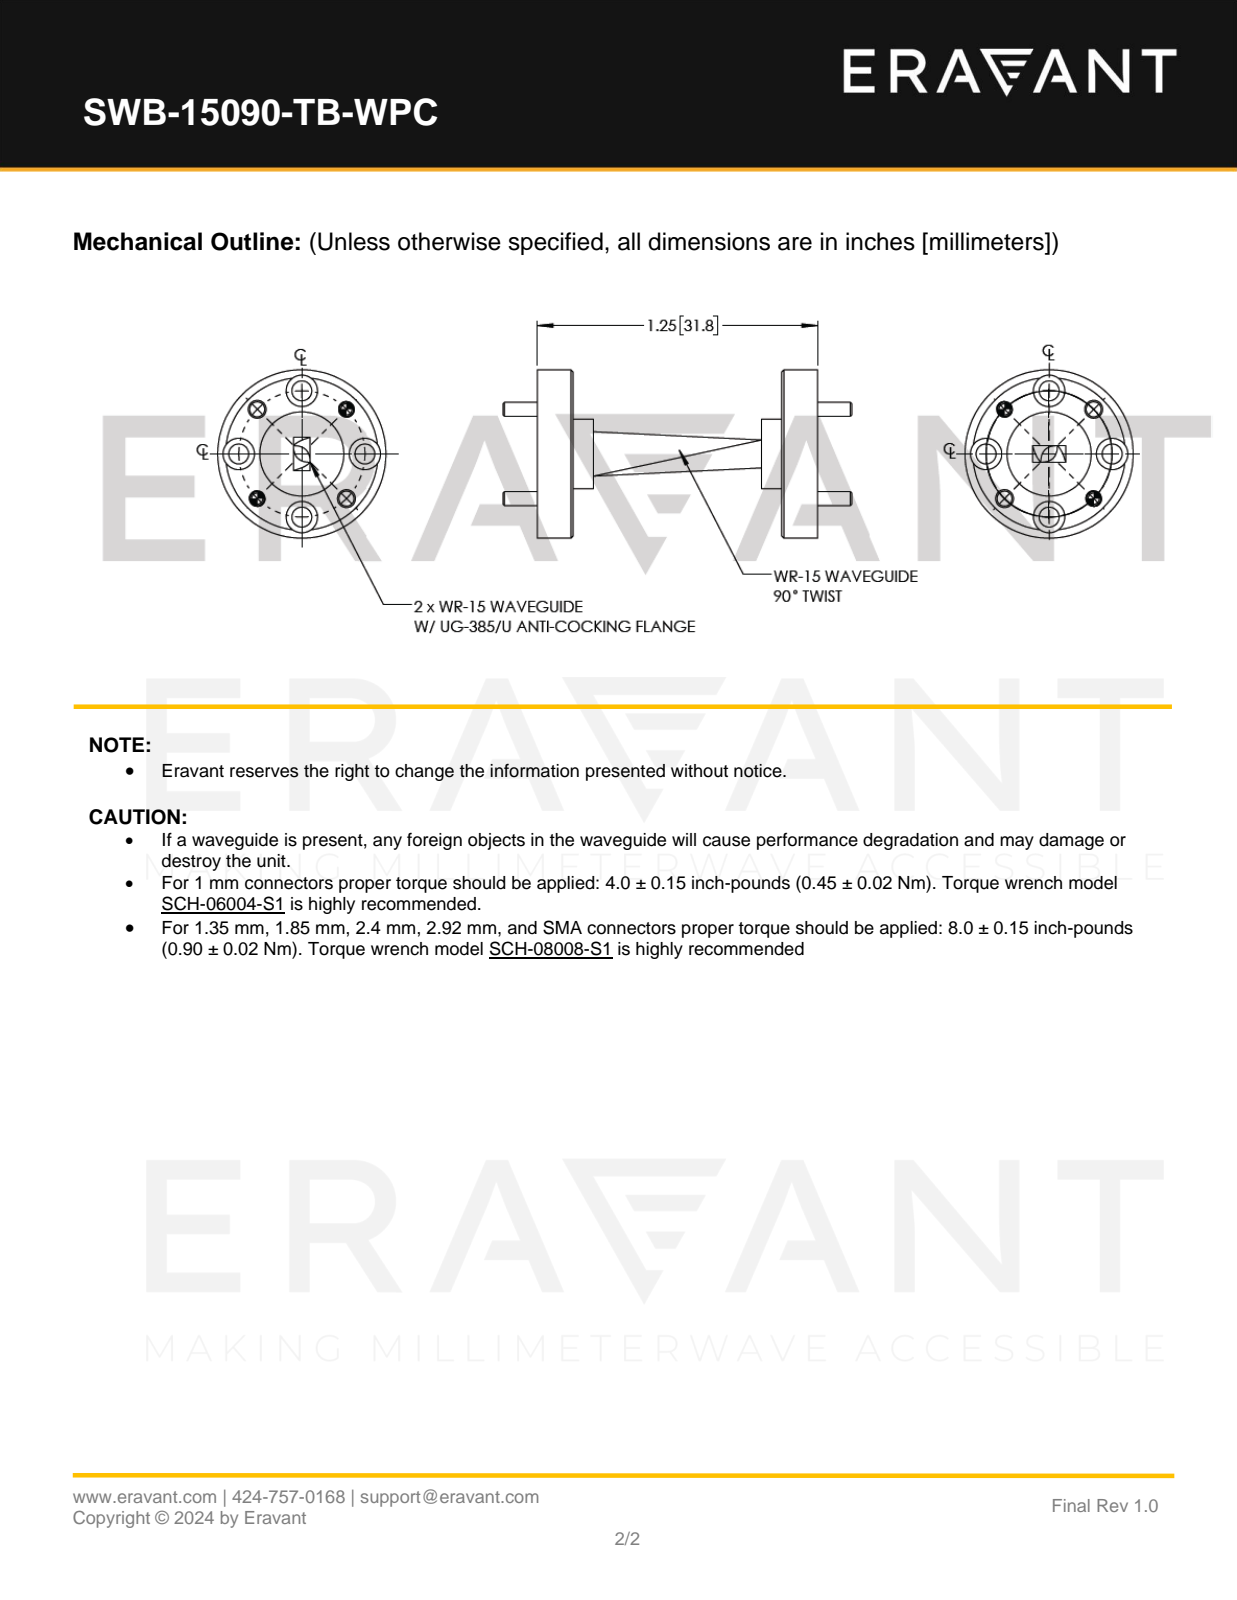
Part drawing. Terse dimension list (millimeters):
name: WB-TV-A
written by: SolidWorks 2021 (AUTOMOTIVE_DESIGN)
unit: mm
bodies: 5 solids, 156 faces (36 planar, 76 cylindrical, 44 other)
size: 39.5 × 19.1 × 19.1
volume: 2 410 mm³; area: 2 468 mm²
holes: 7× ⌀3.6, 4× ⌀2.3, 2× ⌀1.5, 2× ⌀1.7, 1× ⌀17.3
bosses: 2× ⌀1.6, 1× ⌀19.1, 1× ⌀9.5, 1× ⌀7.9
face distances: 3.6, 27.2, 23.6, 30.7, 31.2, 27.7, 4.1, 0.5, 0.5, 4.1
hole spacings: 10.1, 5.5, 13.2, 7.1, 14.3, 13.2, 5.5, 7.1
